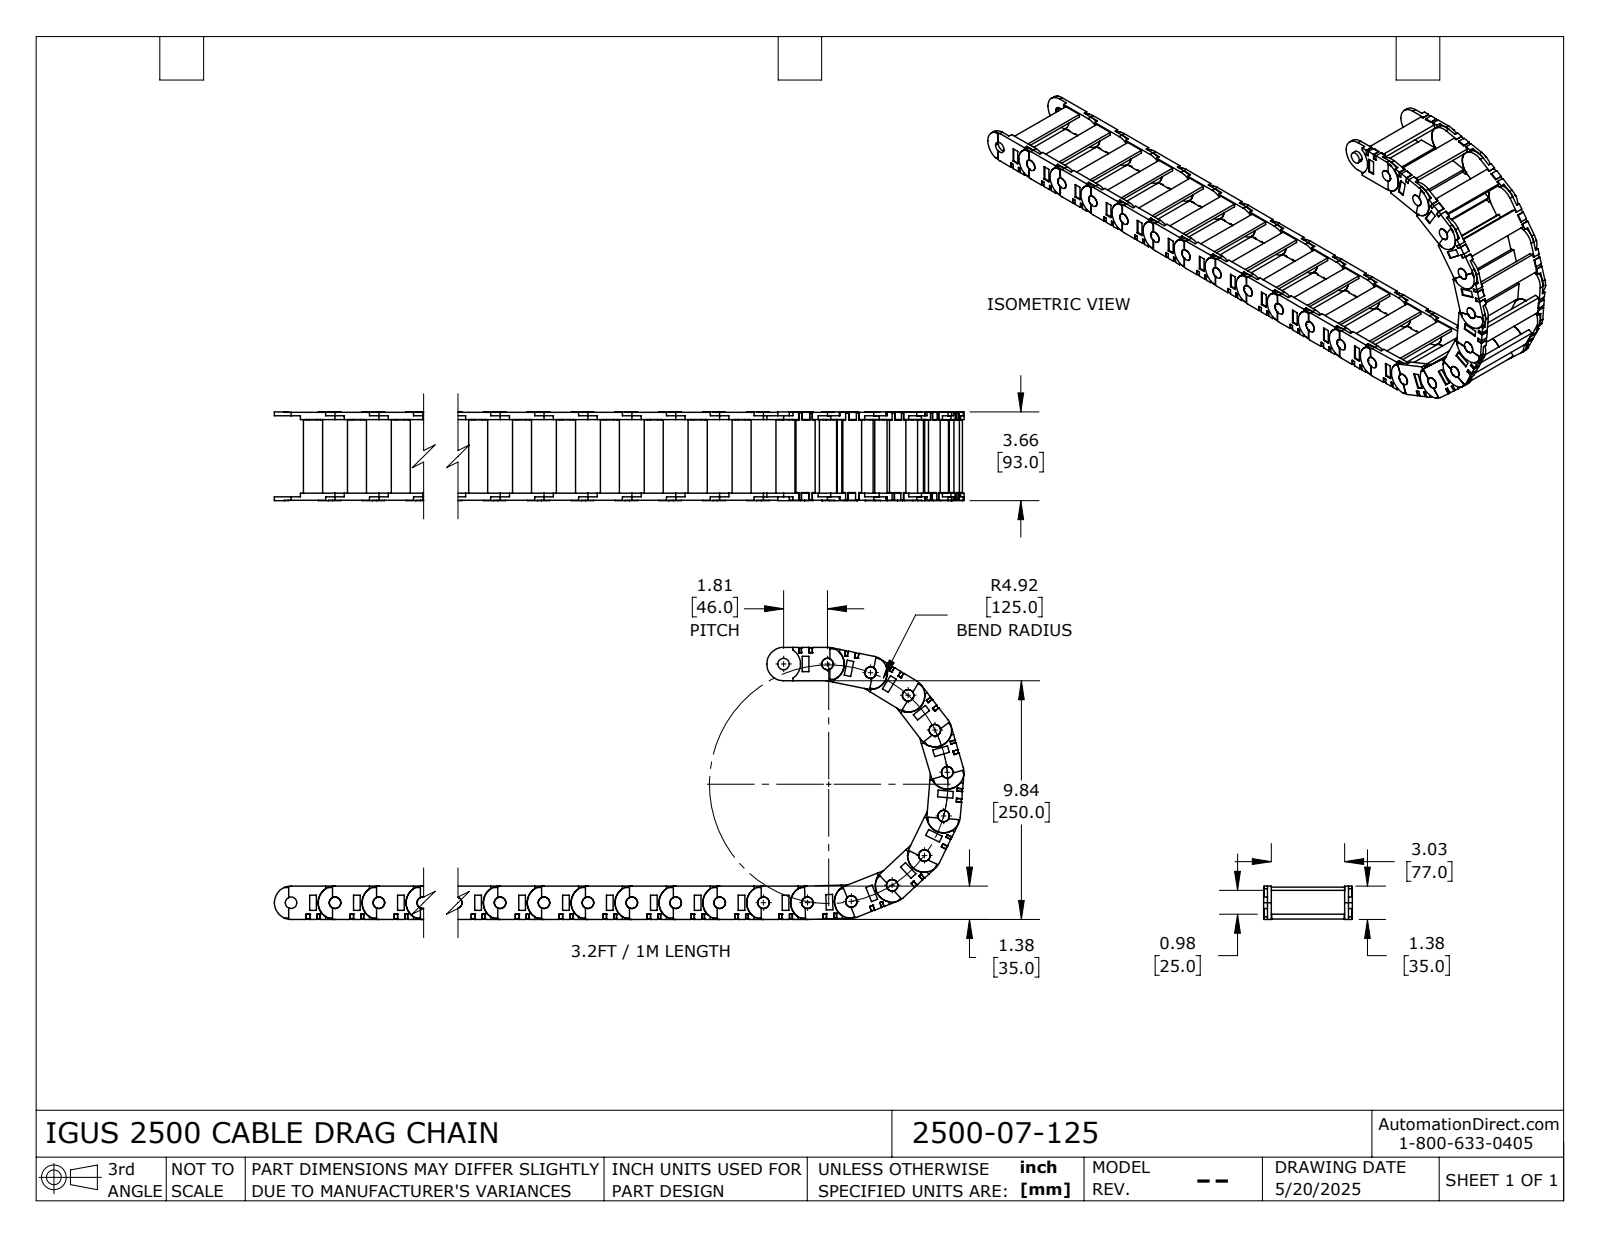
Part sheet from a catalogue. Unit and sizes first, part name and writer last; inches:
Units: inches
Overall size (bounding box): 28.879 × 11.22 × 3.661
Round holes (diameter × count): ⌀0.473 ×22
Round bosses / shafts (diameter × count): ⌀0.472 ×22, ⌀1.378 ×21
Partial cylindrical surfaces — rounded edges, fillets, slot ends (radius × count): R0.697 ×23, R0.689 ×2
Main face-to-face distances: 0.157, 3.189, 3.346, 0.142, 0.299, 3.331, 3.488, 0.197, 0.134, 3.031
Hole centre spacings: 1.811, 3.622, 5.433, 7.244, 9.055, 10.866, 12.677, 3.56
Volume: 49.69 in³ · Surface area: 729.9 in²
Bodies: 66 solids, 2398 faces (1870 planar, 528 cylindrical, 0 other)
Part name (STEP PRODUCT): 2500_07_125
STEP written by: SolidWorks 2024 (AUTOMOTIVE_DESIGN)
